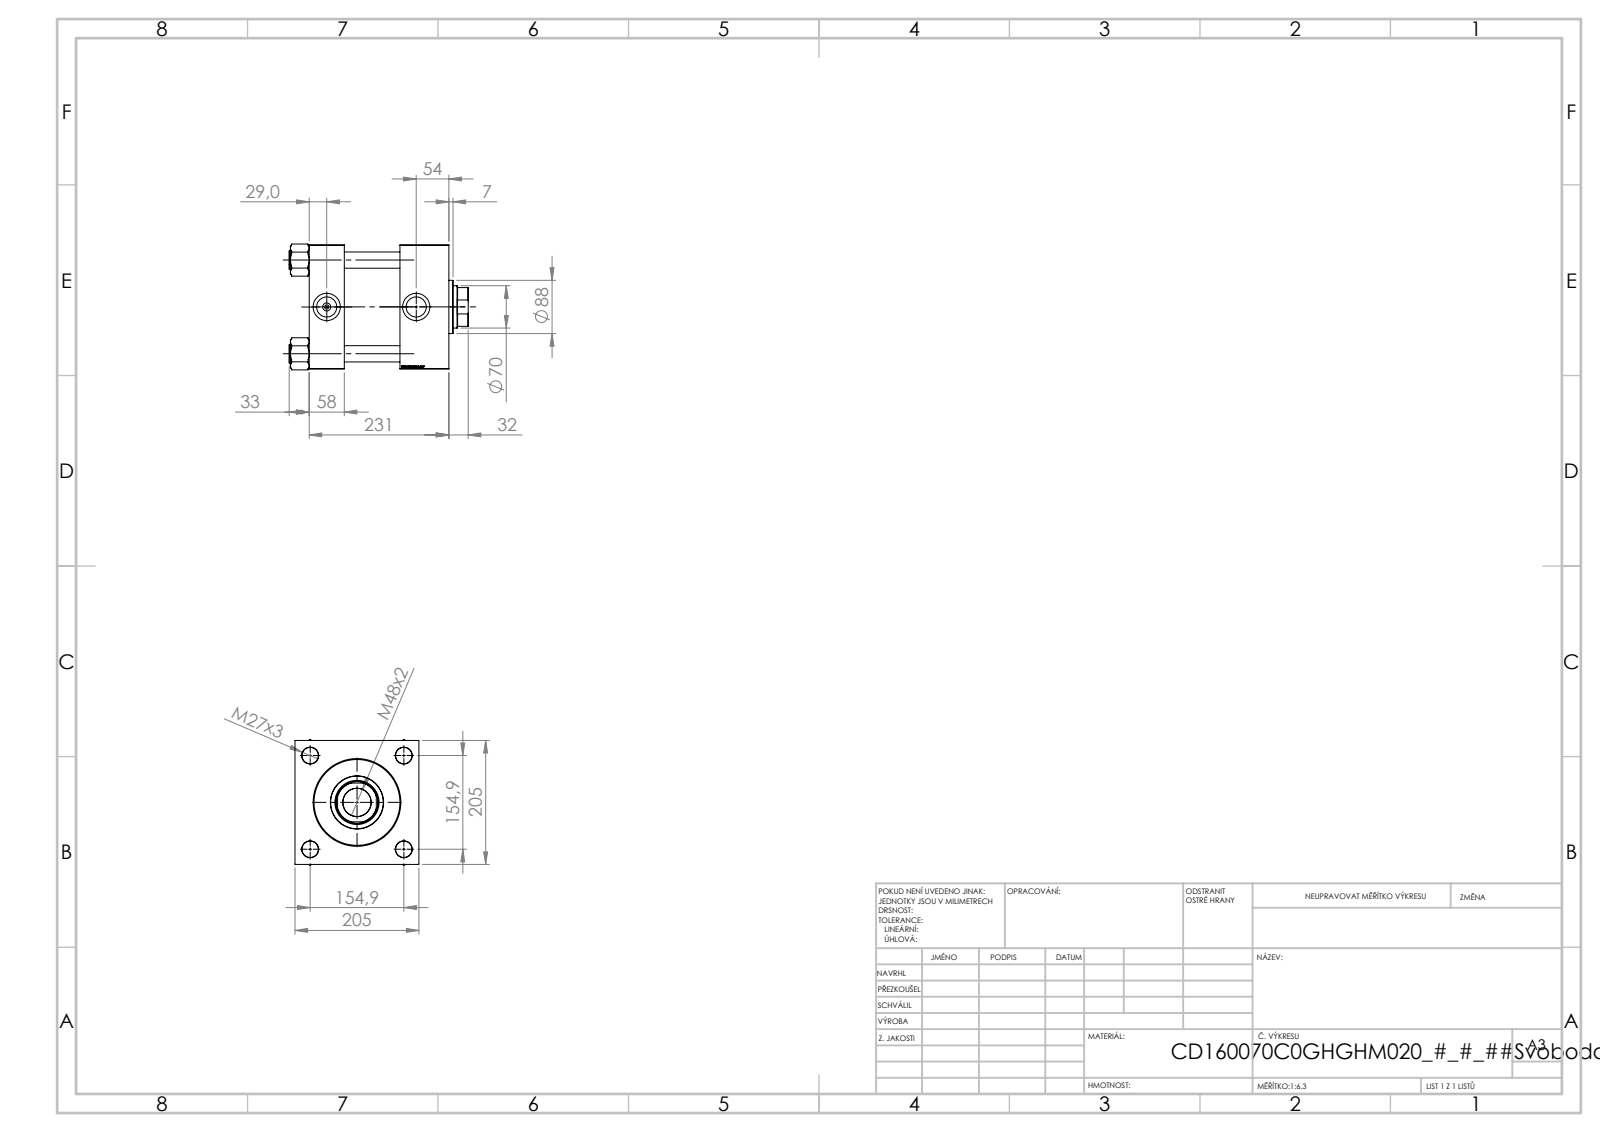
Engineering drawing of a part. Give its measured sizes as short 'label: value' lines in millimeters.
name: NUT_M5_V215CD_C; V215CD_VCP_C; V215CD_Body_C; V215CD_VC_C (+1 more)
written by: SolidWorks 2019 (CONFIG_CONTROL_DESIGN)
unit: mm
bodies: 11 solids, 1196 faces (574 planar, 86 cylindrical, 536 other)
size: 296 × 208.14 × 205
volume: 7 447 000 mm³; area: 694 274 mm²
holes: 4× ⌀27, 2× ⌀7, 2× ⌀33.24, 2× ⌀45, 1× ⌀46.5, 1× ⌀70, 1× ⌀73, 1× ⌀120, 1× ⌀142, 1× ⌀160
bosses: 4× ⌀30, 1× ⌀166, 1× ⌀88
rounds: 1× R34
face distances: 205, 58, 231, 173, 150, 92, 81, 202.3, 144.3, 52.3
hole spacings: 109.53, 154.9, 219.06, 148
